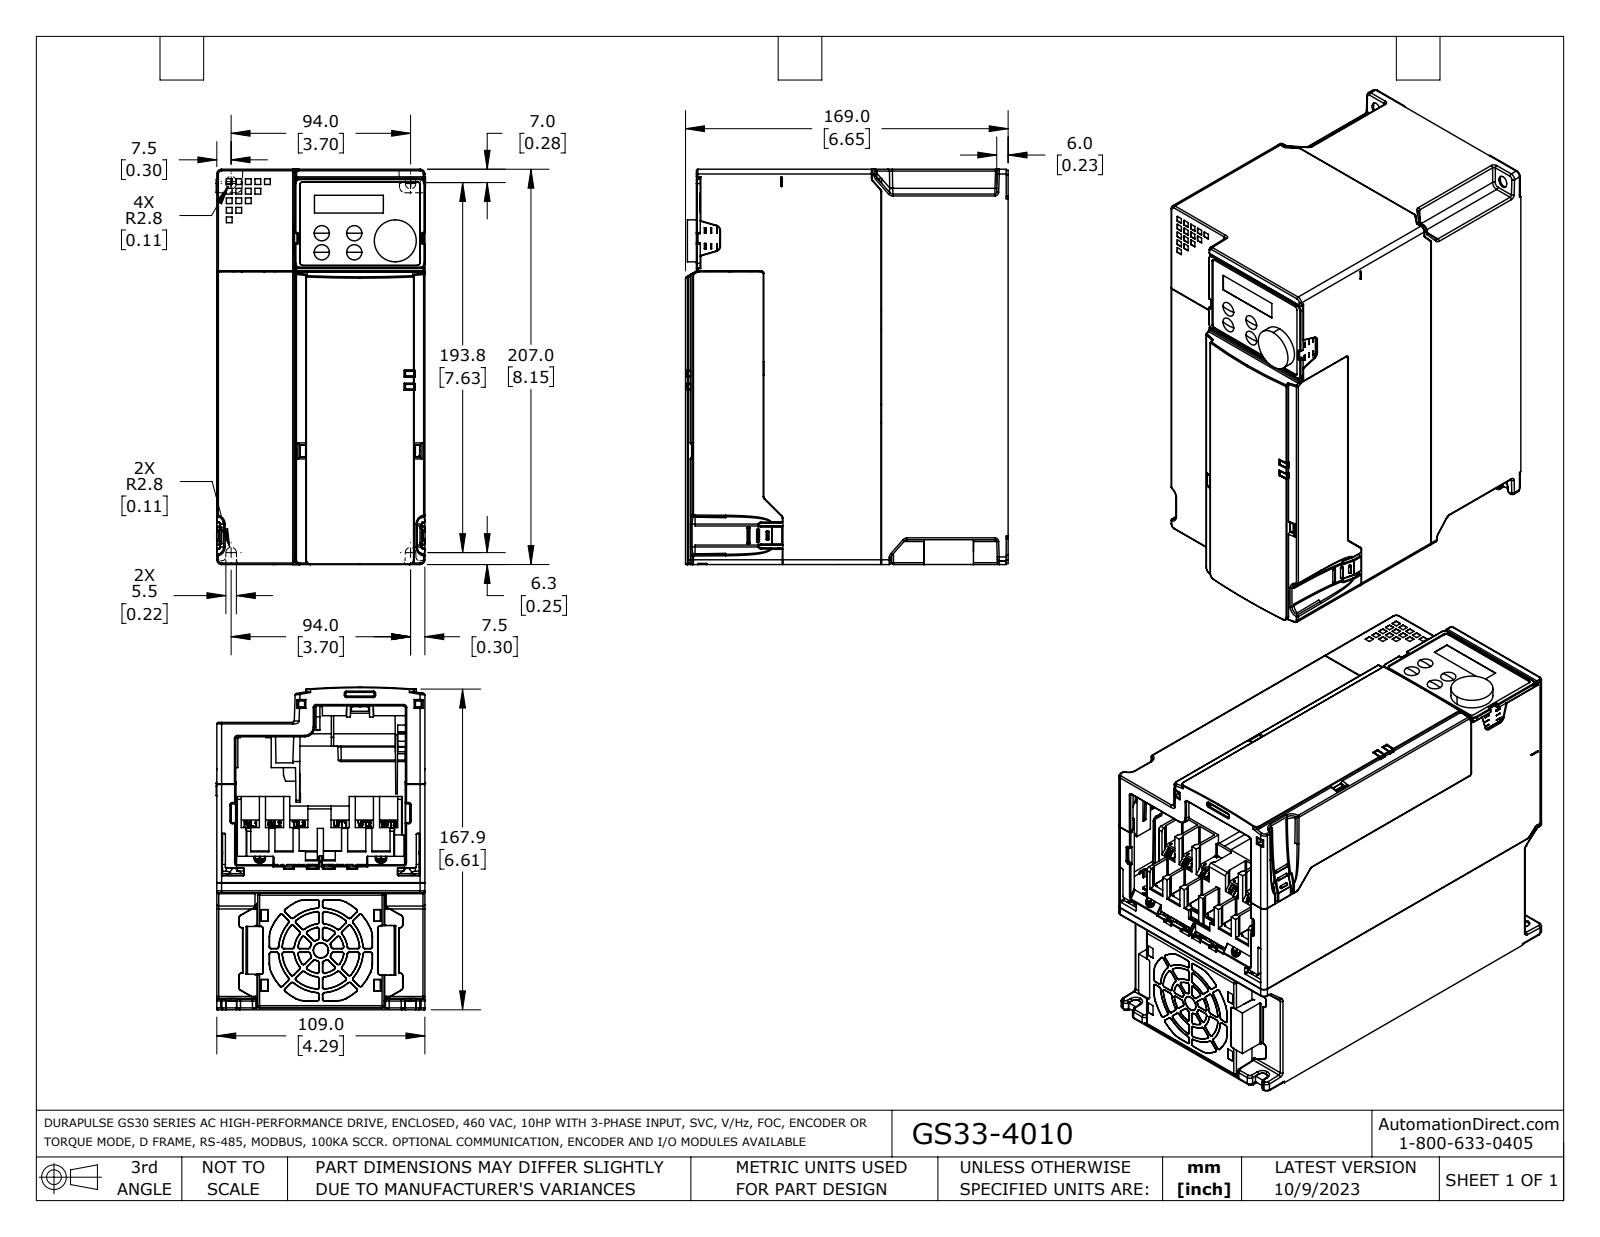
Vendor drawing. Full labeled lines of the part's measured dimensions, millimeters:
Part name (STEP PRODUCT): vfd-mh300-d1-pd-3d01 gpr1 red1 33 top covr n knob ext1bb r1-kn sfr1b wo FG Mod1a sr1c fxtrd1C fxt
STEP written by: SolidWorks 2021 (AUTOMOTIVE_DESIGN)
Units: millimetres
Bodies: 7 solids, 4476 faces (2524 planar, 995 cylindrical, 957 other)
Overall size (bounding box): 207 × 169 × 111.9
Volume: 1 722 000 mm³ · Surface area: 351 500 mm²
Round holes (diameter × count): ⌀2.5 ×4, ⌀2.2 ×2, ⌀18 ×1
Round bosses / shafts (diameter × count): ⌀22 ×1
Partial cylindrical surfaces — rounded edges, fillets, slot ends (radius × count): R0.5 ×187, R1 ×147, R0.3 ×87, R2 ×40, R0.8 ×32, R0.4 ×26, R1.5 ×19, R0.2 ×17
Main face-to-face distances: 109, 1, 65.6, 66.6, 2.5, 106.5, 2.6, 103.9, 106.4, 150.5
Hole centre spacings: 12.6, 27.3, 34.4, 34.4, 47, 54.2, 55.4, 56.9
